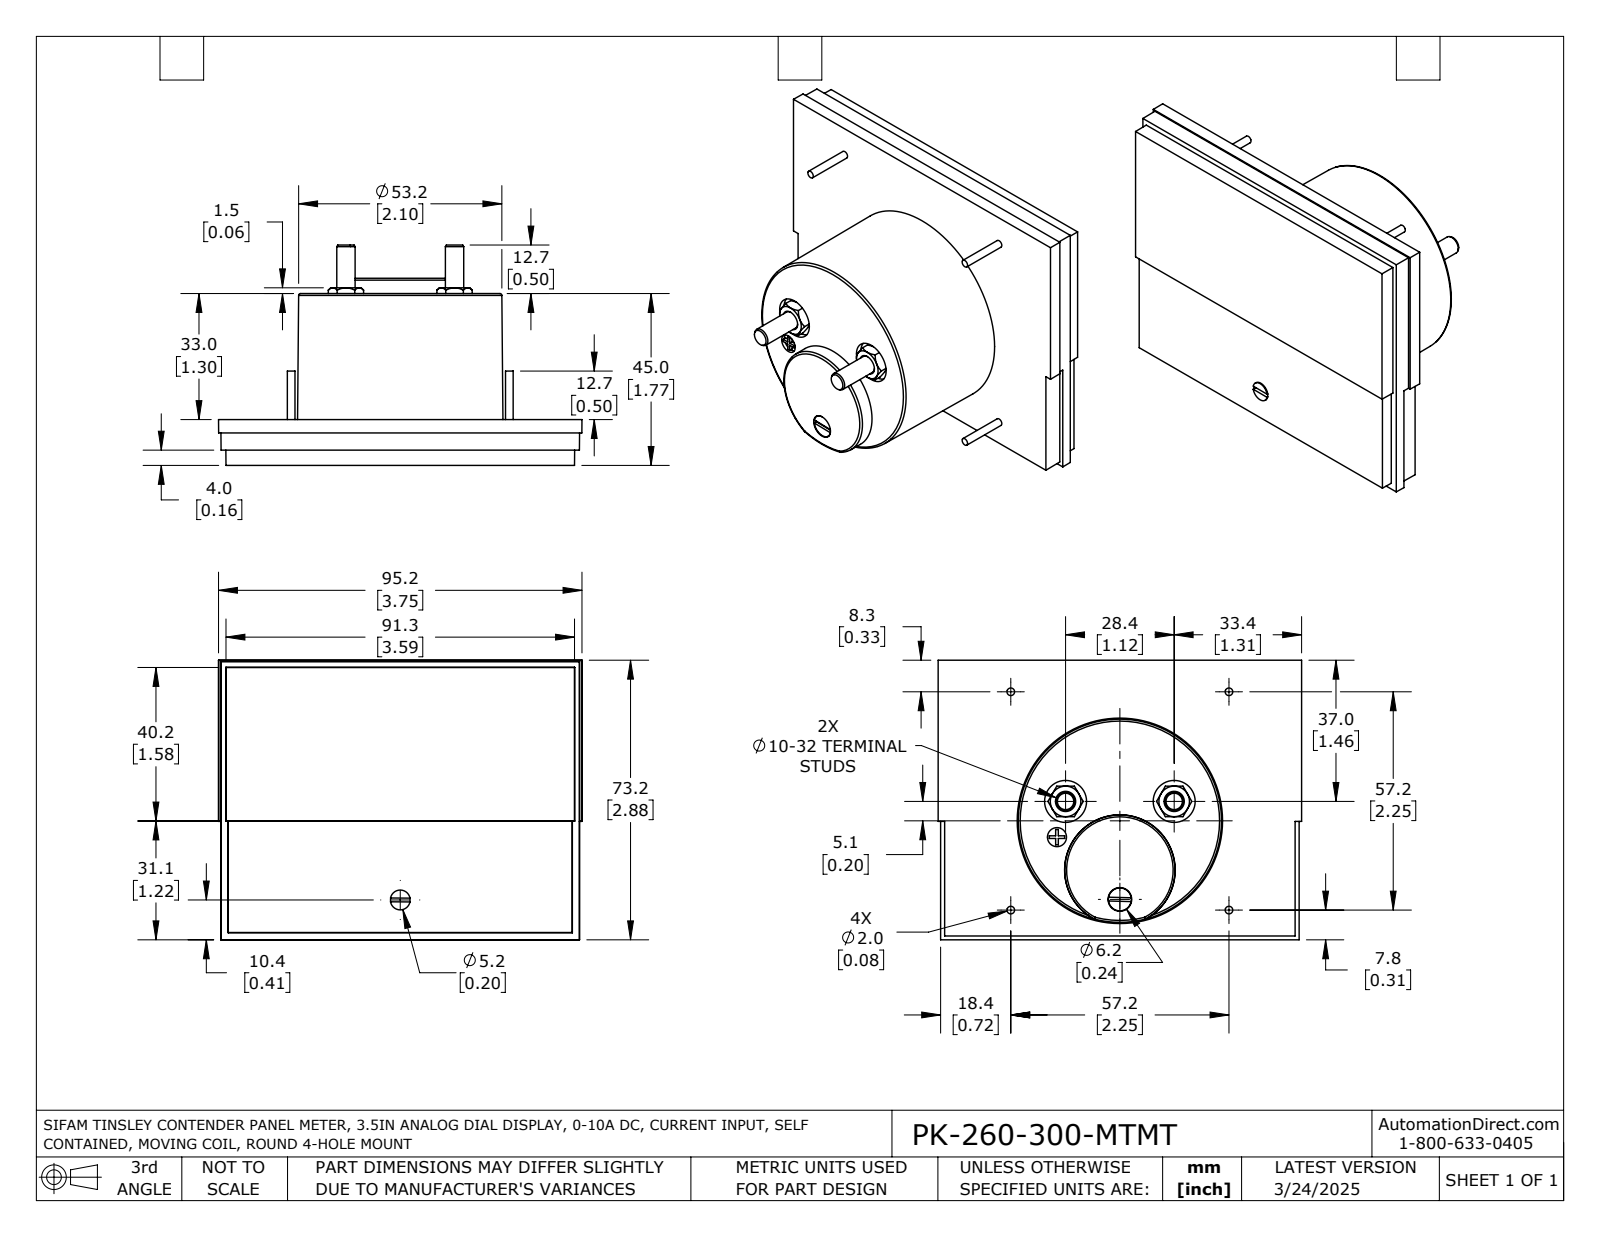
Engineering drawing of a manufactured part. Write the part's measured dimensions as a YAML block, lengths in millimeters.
part_name: "PK-260-300-MTMT"
step_written_by: "SolidWorks 2021 (AUTOMOTIVE_DESIGN)"
units: millimeters
bodies: {solids: 1, faces: 163, planar: 76, cylindrical: 31, other: 56}
overall_size: [95.2, 73.2, 57.7]
volume: 154800
surface_area: 24770
round_holes:
  - {diameter: 11, count: 2}
  - {diameter: 5, count: 1}
  - {diameter: 6.2, count: 1}
round_bosses_or_shafts:
  - {diameter: 2, count: 4}
  - {diameter: 4.8, count: 2}
  - {diameter: 6, count: 1}
  - {diameter: 5.2, count: 1}
partial_cylinders:
  - {radius: 2.5, count: 1}
face_to_face_distances: [12, 0.8, 11.3, 45, 33, 44.2, 4, 1.9, 8, 37]
hole_center_spacings: [29.3, 9.6, 23.2, 28.4, 32.1]
